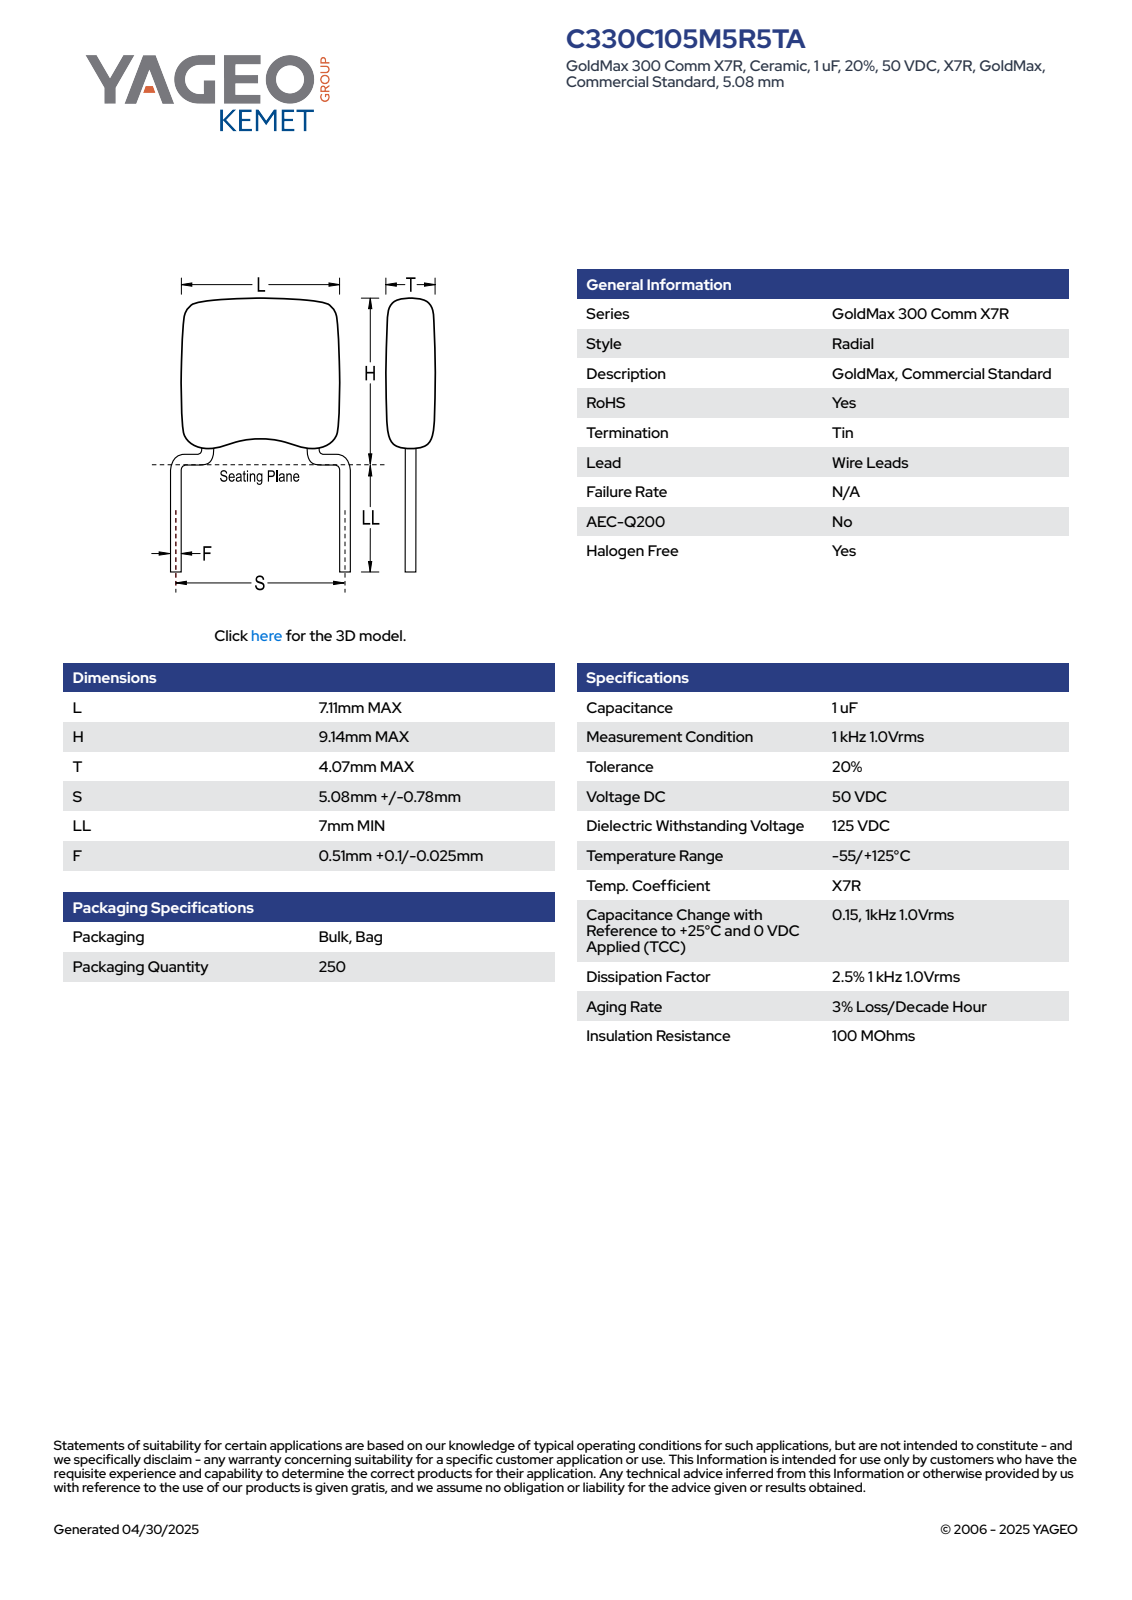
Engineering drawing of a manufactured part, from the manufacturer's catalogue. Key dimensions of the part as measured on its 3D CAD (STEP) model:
Part name (STEP PRODUCT): CCR_SB_7.11X9.14_L7.11H9.14T4.07S5.08LL7F0.51
STEP written by: SolidWorks 2014 (AUTOMOTIVE_DESIGN)
Units: millimetres
Bodies: 4 solids, 97 faces (65 planar, 14 cylindrical, 18 other)
Overall size (bounding box): 16.14 × 7.11 × 4.08
Volume: 186 mm³ · Surface area: 215 mm²
Round bosses / shafts (diameter × count): ⌀0.51 ×2
Partial cylindrical surfaces — rounded edges, fillets, slot ends (radius × count): R1 ×10
Main face-to-face distances: 4.07, 7.11, 6.73, 4.08, 3.69, 3.04, 3.09, 0.6, 3.64, 0.61
